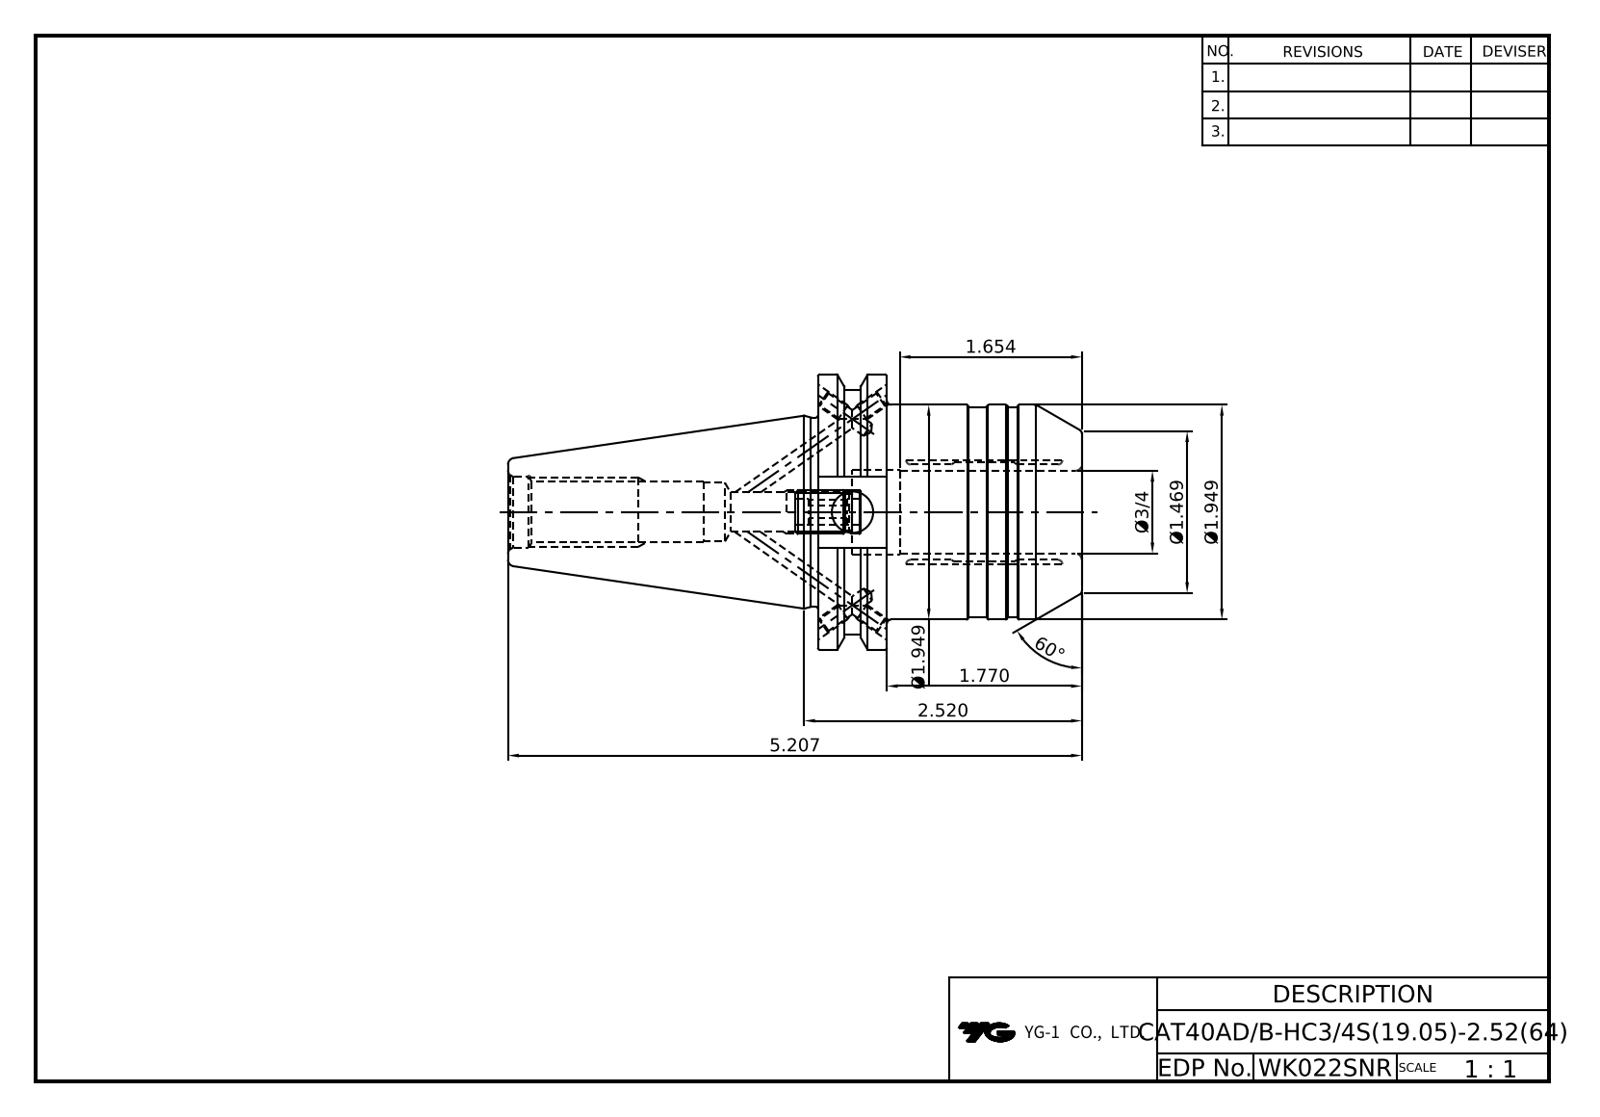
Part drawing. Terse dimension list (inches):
name: LO-CAT40ADB-HC19.05S-64
written by: Autodesk Inventor 2025 (AUTOMOTIVE_DESIGN)
unit: in
bodies: 1 solid, 104 faces (34 planar, 31 cylindrical, 39 other)
size: 5.207 × 2.5 × 2.405
volume: 10.37 in³; area: 46.27 in²
holes: 4× ⌀0.128, 4× ⌀0.157, 1× ⌀0.351, 1× ⌀0.375, 1× ⌀0.527, 1× ⌀0.642, 1× ⌀0.75, 1× ⌀0.764
bosses: 1× ⌀2.5, 1× ⌀2.217, 1× ⌀1.949, 1× ⌀1.909, 1× ⌀1.717
rounds: 1× R0.322
face distances: 2.395, 0.625, 1.77, 0.308, 0.317, 2.087, 1.874, 0.645, 2.812, 3.12
hole spacings: 1.383
